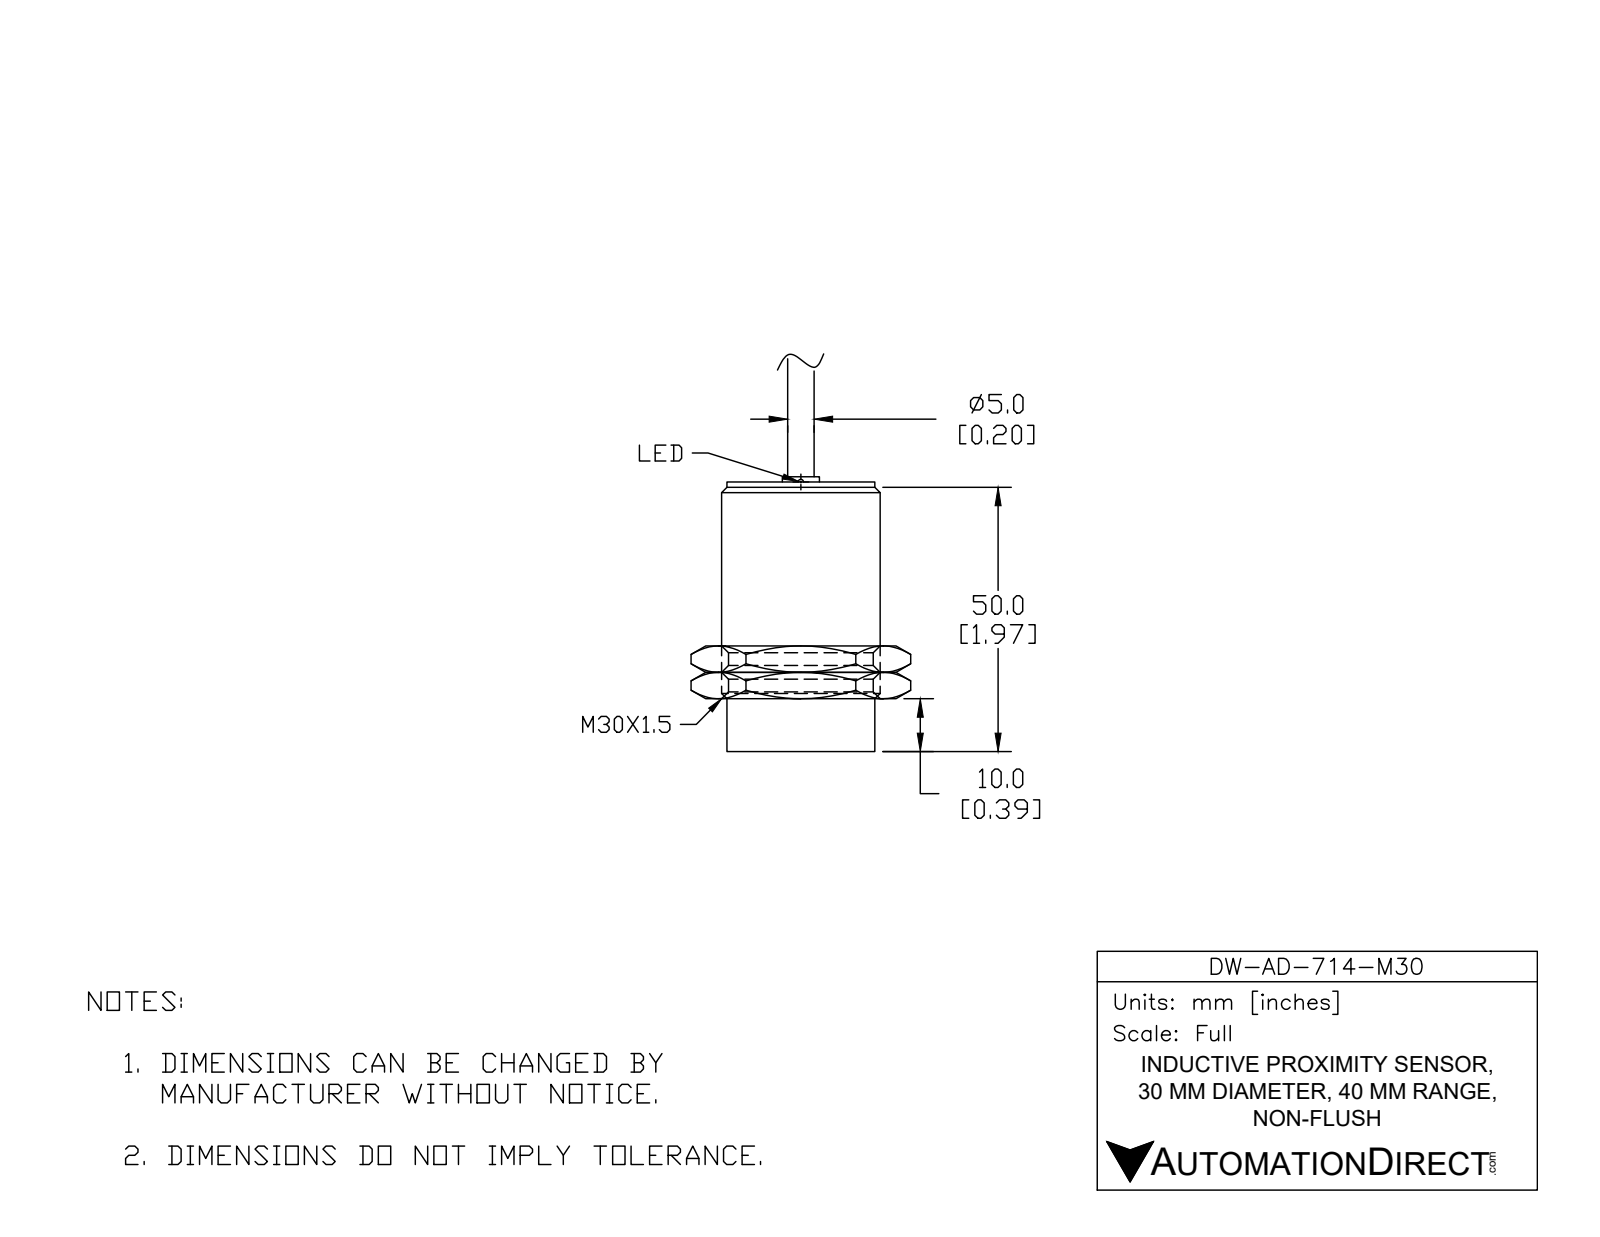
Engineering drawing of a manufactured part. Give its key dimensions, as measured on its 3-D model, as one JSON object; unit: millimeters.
{"part_name": "DW-AD-714-M30", "step_written_by": "SolidWorks 2017 (AUTOMOTIVE_DESIGN)", "units": "millimeters", "bodies": {"solids": 2, "faces": 37, "planar": 18, "cylindrical": 7, "other": 12}, "overall_size": [76.6, 30, 30], "volume_mm3": 35380, "surface_area_mm2": 6516, "round_bosses_or_shafts": [[30, 1], [27.5, 1], [10.5, 1], [6.8, 1], [5, 1], [3, 1]], "face_to_face_distances": [51, 0.8, 53, 2, 51.8, 1.2, 48, 3, 3.8, 5]}
